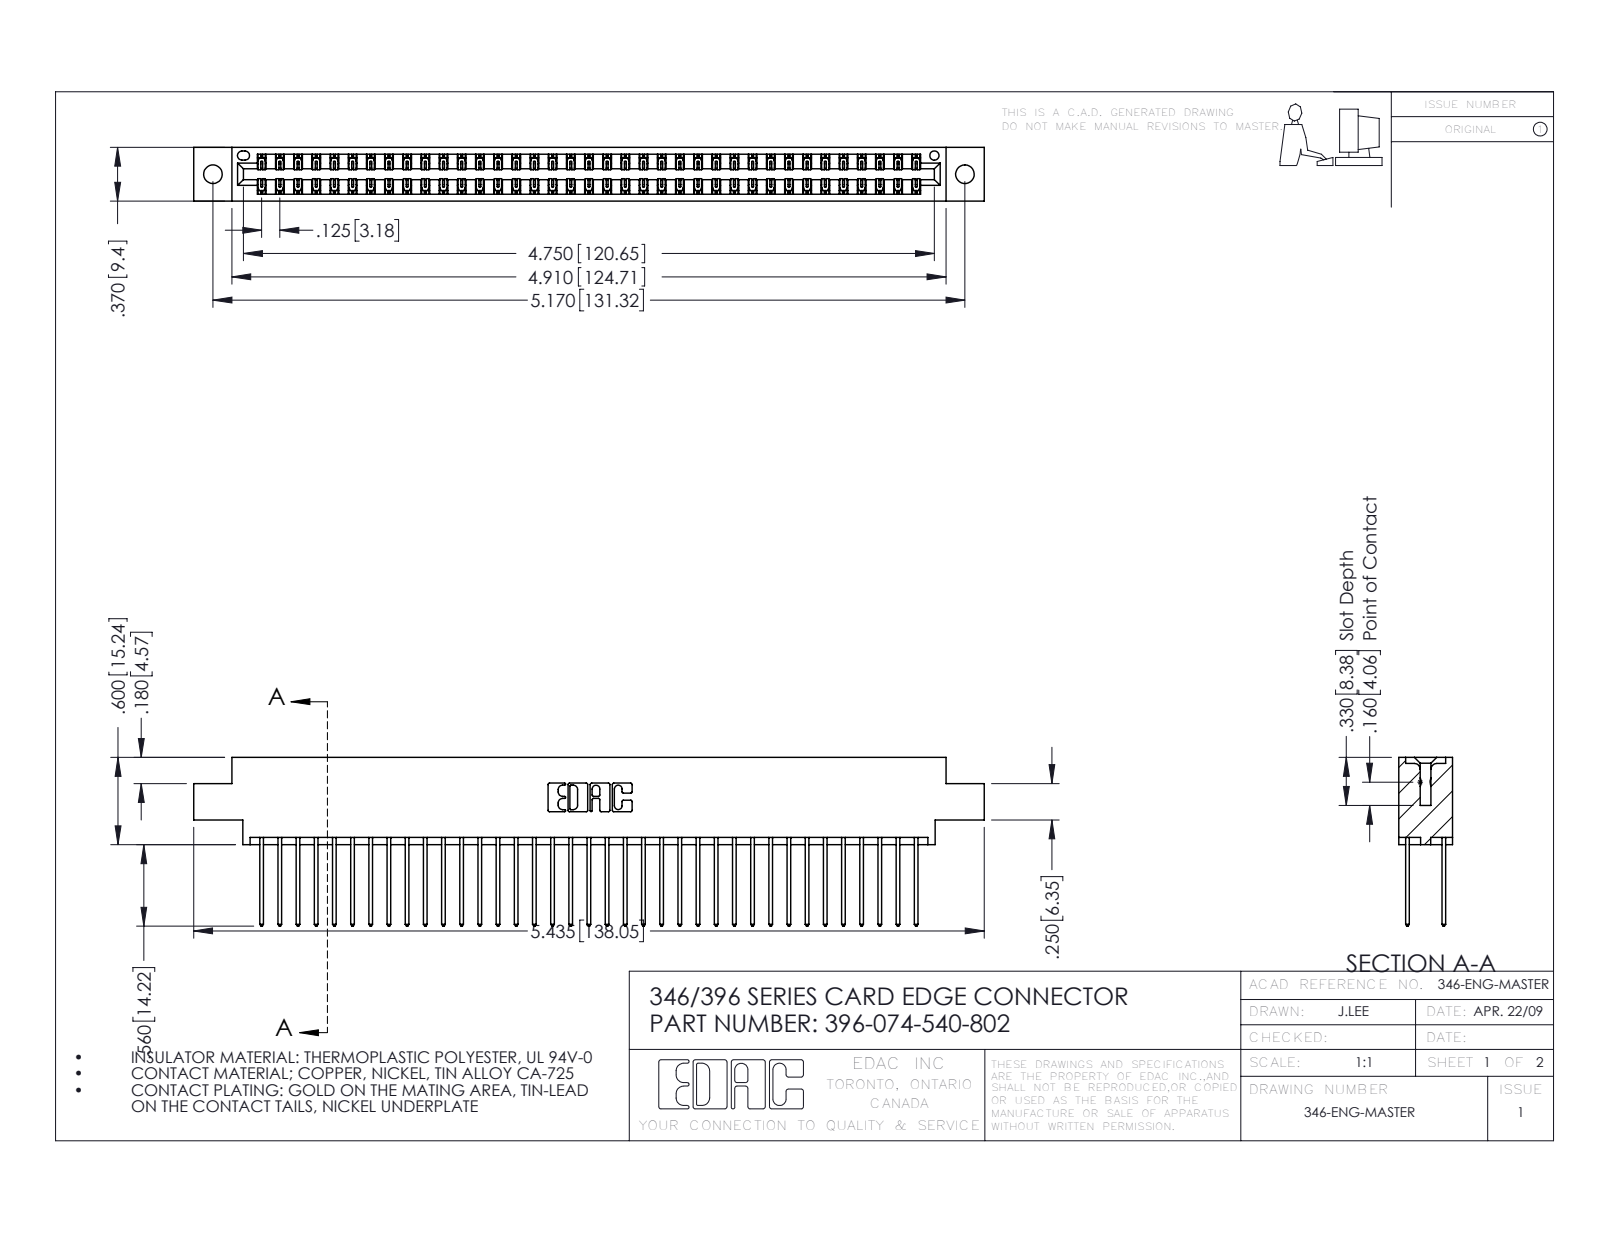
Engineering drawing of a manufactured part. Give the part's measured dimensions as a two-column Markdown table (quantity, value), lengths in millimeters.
| quantity | value |
| --- | --- |
| part name | 346 Part_0.170 Offset - 0.128 Dia; 345-292-001_345-293-140; 396-074-540-802 |
| STEP written by | SolidWorks 2016 (CONFIG_CONTROL_DESIGN) |
| units | millimeters |
| bodies | 75 solids, 3974 faces (2670 planar, 1304 cylindrical, 0 other) |
| overall size | 138 × 29.5 × 9.4 |
| volume | 13 500 mm³ |
| surface area | 19 730 mm² |
| round holes (diameter × count) | 3.3 × 2, 1.6 × 1 |
| partial cylindrical surfaces (radius × count) | 0.2 × 111, 0.3 × 74, 0.3 × 22, 0.2 × 6, 0.8 × 6, 0.7 × 3, 0.4 × 2, 0.6 × 2 |
| main face-to-face distances | 1.2, 8.2, 6.4, 1.8, 7.6, 0.6, 9.4, 7, 3.8, 5.6 |
| hole center spacings | 6.2, 126, 131.3 |
